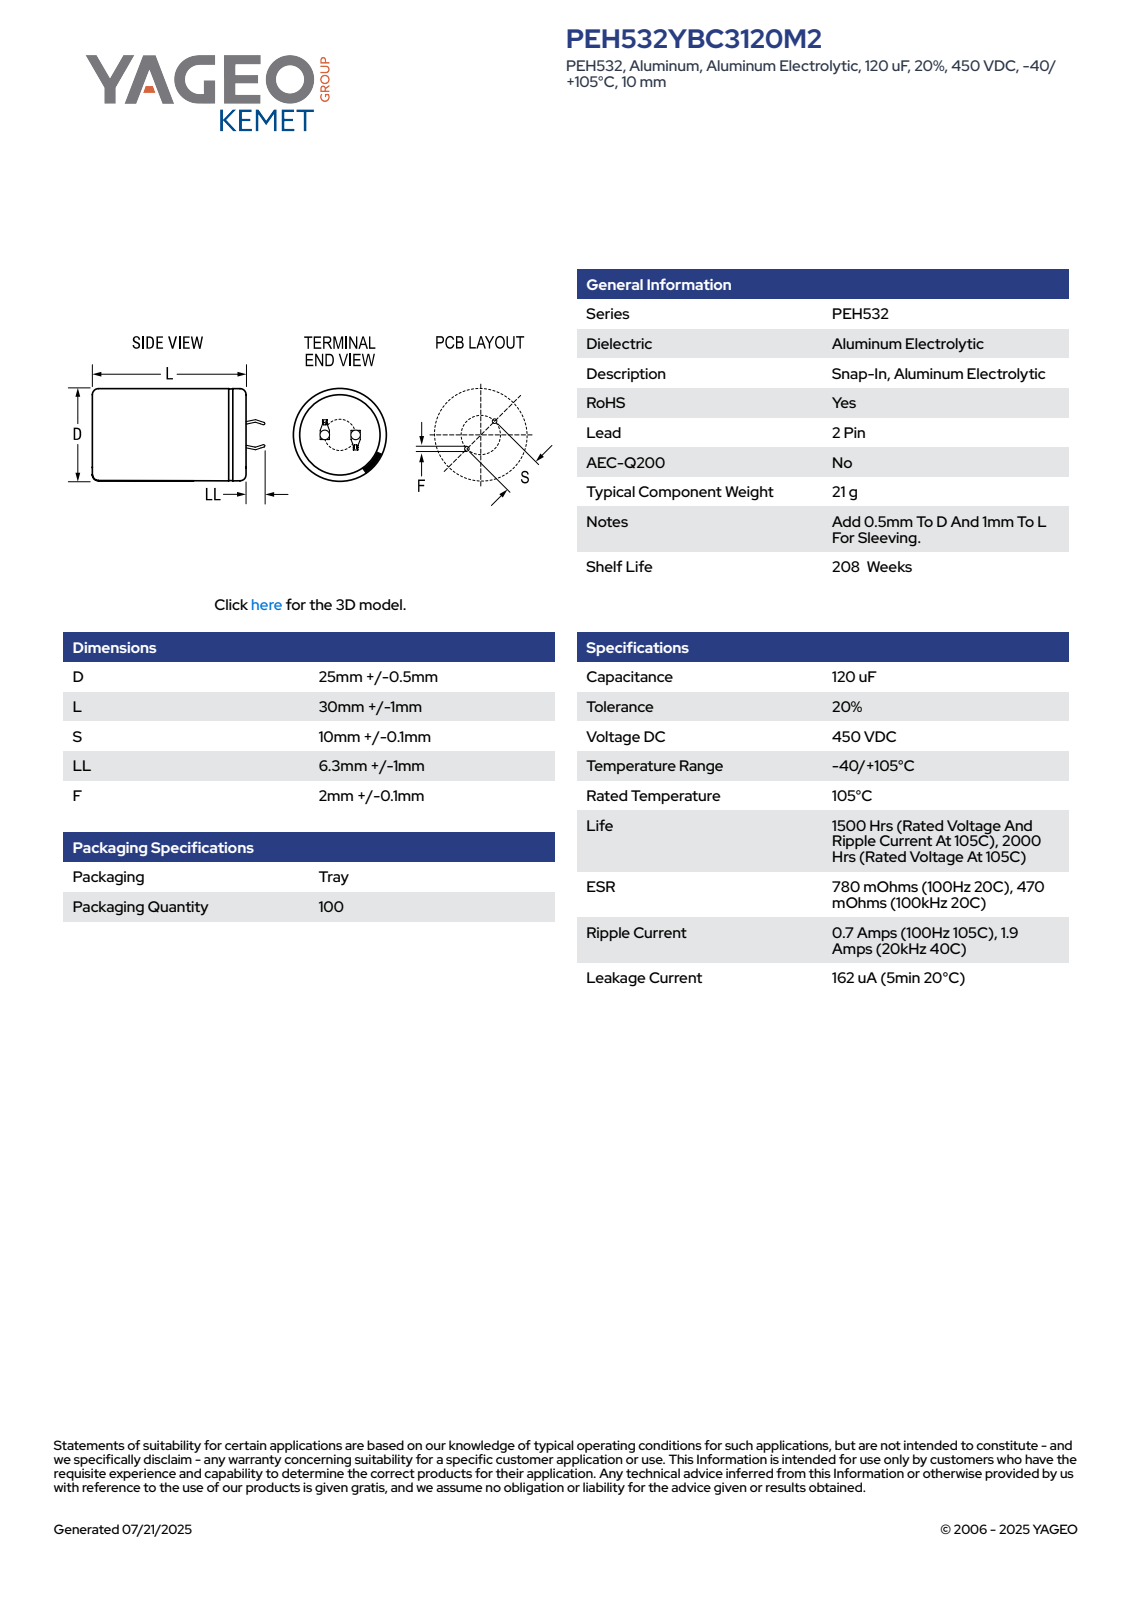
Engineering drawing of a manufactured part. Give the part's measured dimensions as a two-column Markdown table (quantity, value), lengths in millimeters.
| quantity | value |
| --- | --- |
| part name | CARS_K2P_25X30_D25.5L31S10LL7.3F2.1 |
| STEP written by | SolidWorks 2014 (AUTOMOTIVE_DESIGN) |
| units | millimeters |
| bodies | 1 solid, 100 faces (52 planar, 9 cylindrical, 39 other) |
| overall size | 38.29 × 25.5 × 25.5 |
| volume | 15 651 mm³ |
| surface area | 3 527 mm² |
| round holes (diameter × count) | 22.56 × 1 |
| round bosses / shafts (diameter × count) | 25.5 × 1 |
| partial cylindrical surfaces (radius × count) | 12.74 × 1 |
| main face-to-face distances | 30.99, 0.6, 31.49, 0.5, 7.08, 7.64, 0.75, 1.35, 7.68, 6.48 |
